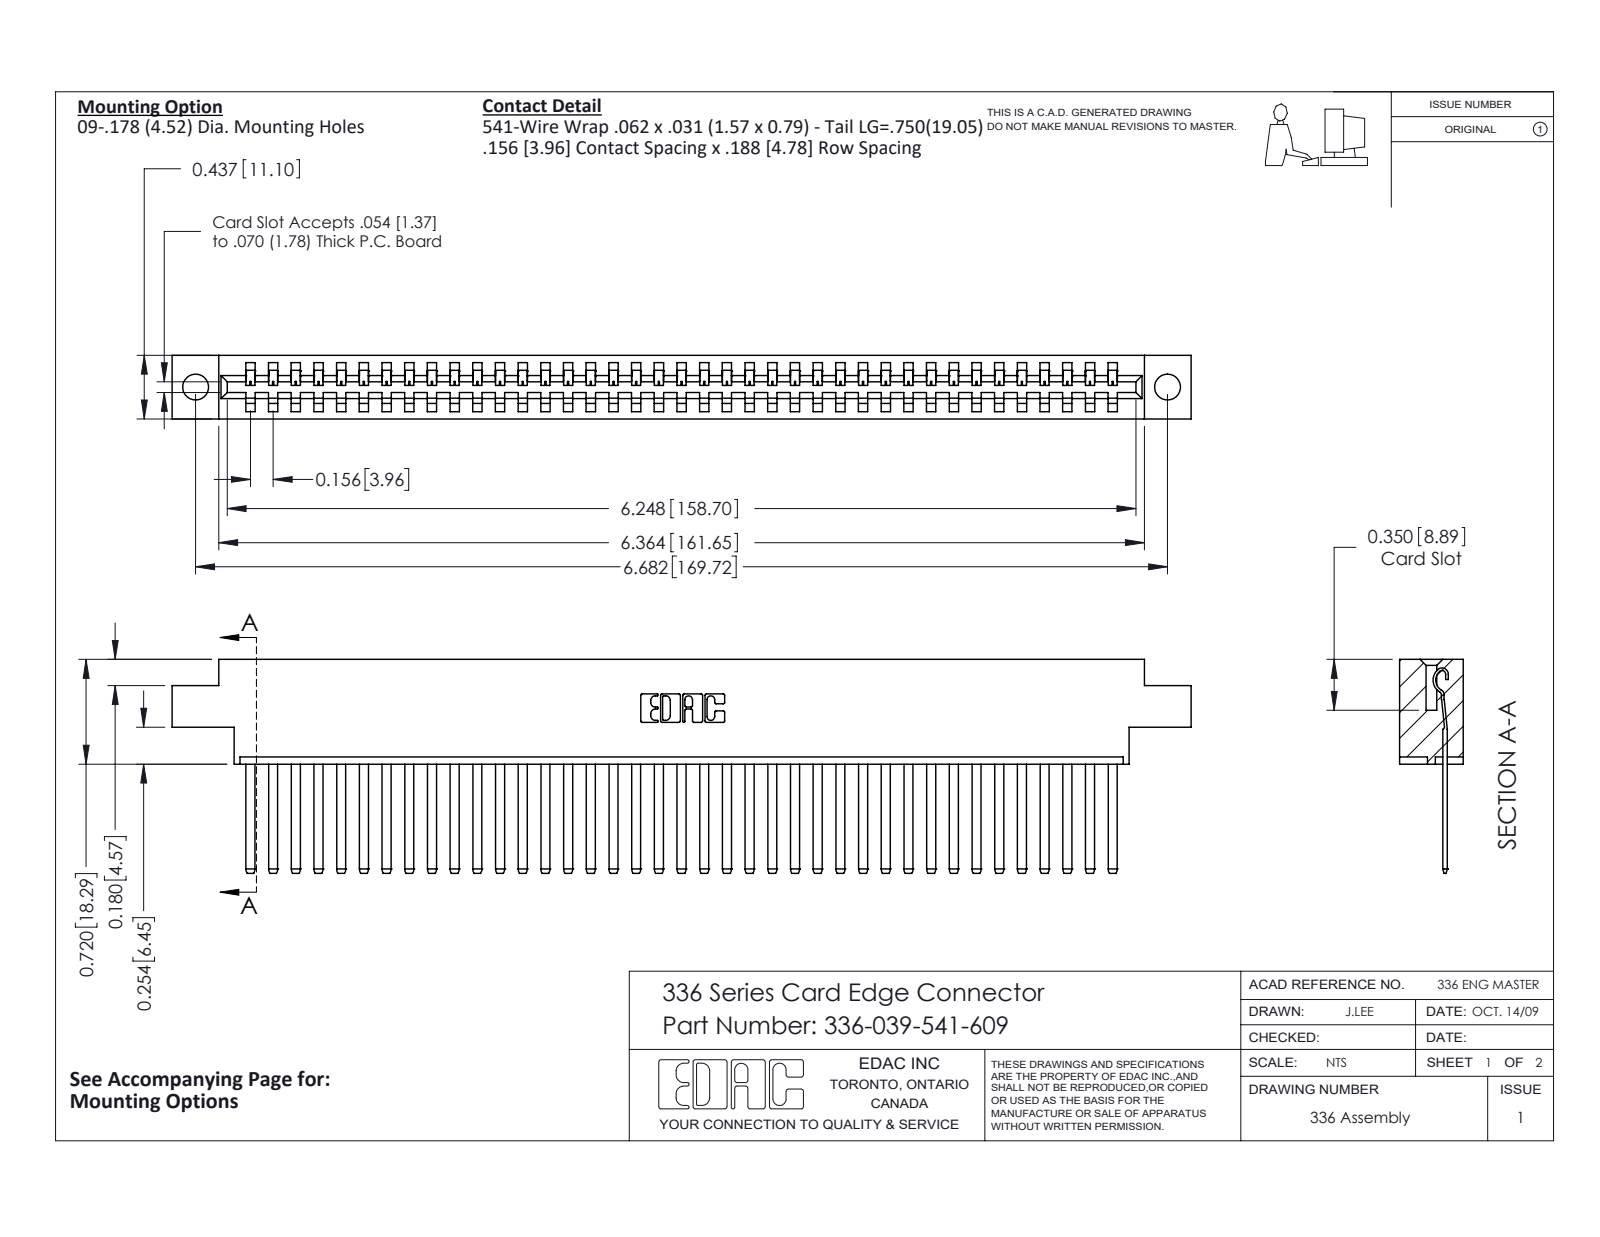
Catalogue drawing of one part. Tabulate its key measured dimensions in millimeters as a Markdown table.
| quantity | value |
| --- | --- |
| part name | 336 Part_Offset - .178 Dia - TH; 336-039-541-609; 336-290-001_336-290-541 |
| STEP written by | SolidWorks 2020 (CONFIG_CONTROL_DESIGN) |
| units | millimeters |
| bodies | 40 solids, 2068 faces (1400 planar, 668 cylindrical, 0 other) |
| overall size | 177.9 × 37.3 × 11.1 |
| volume | 25 690 mm³ |
| surface area | 27 880 mm² |
| round holes (diameter × count) | 4.5 × 2 |
| partial cylindrical surfaces (radius × count) | 0.1 × 78, 1.4 × 78, 0.3 × 22, 0.2 × 6, 0.8 × 6, 0.7 × 3, 0.6 × 2, 1 × 2 |
| main face-to-face distances | 11.1, 4.6, 8.3, 3.6, 7.5, 2.8, 0.8, 6.5, 1.3, 9.8 |
| hole center spacings | 169.7 |
